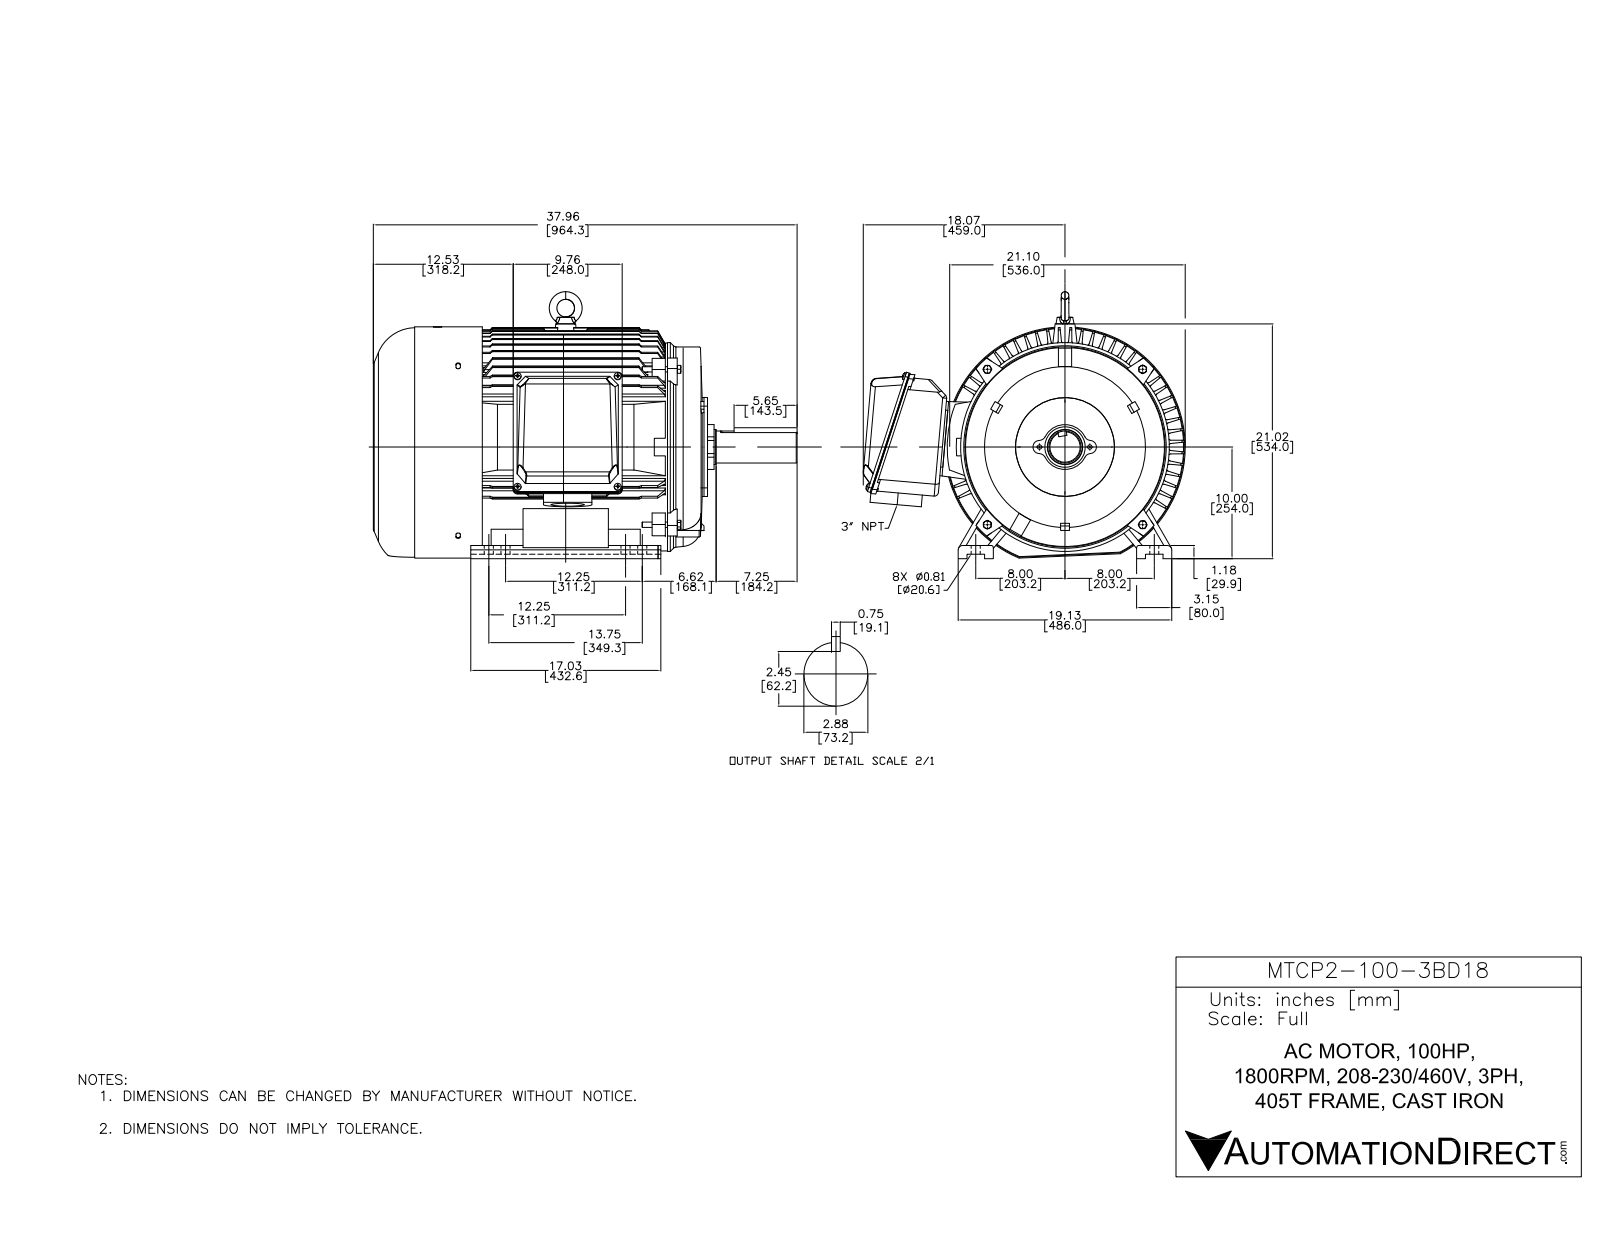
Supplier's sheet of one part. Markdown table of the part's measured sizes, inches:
| quantity | value |
| --- | --- |
| part name | PEWWE-405T-4,6 |
| STEP written by | SolidWorks 2017 (AUTOMOTIVE_DESIGN) |
| units | inches |
| bodies | 20 solids, 3934 faces (1812 planar, 1817 cylindrical, 305 other) |
| overall size | 37.965 × 28.846 × 23.913 |
| volume | 1 745 in³ |
| surface area | 8 451 in² |
| round holes (diameter × count) | 0.394 × 14, 0.827 × 8, 0.315 × 4, 0.472 × 4, 0.748 × 2, 0.453 × 1, 0.709 × 1, 1.024 × 1, 3 × 1, 3.622 × 1, 8.782 × 1, 17.52 × 1 |
| round bosses / shafts (diameter × count) | 0.63 × 4, 0.276 × 4, 21.535 × 1, 21.26 × 1, 18.699 × 1, 18.622 × 1, 18.031 × 1, 8.861 × 1 |
| partial cylindrical surfaces (radius × count) | 0.02 × 1078, 0.197 × 76, 0.394 × 12, 0.354 × 11, 0.079 × 8, 0.591 × 6, 0.787 × 4, 0.118 × 2 |
| main face-to-face distances | 0.059, 0.236, 0.079, 0.787, 0.354, 1.181, 29.448, 29.507, 29.802, 29.861 |
| hole center spacings | 8.976, 10.433, 1.5, 12.252, 13.763, 13.764, 13.919, 16 |
